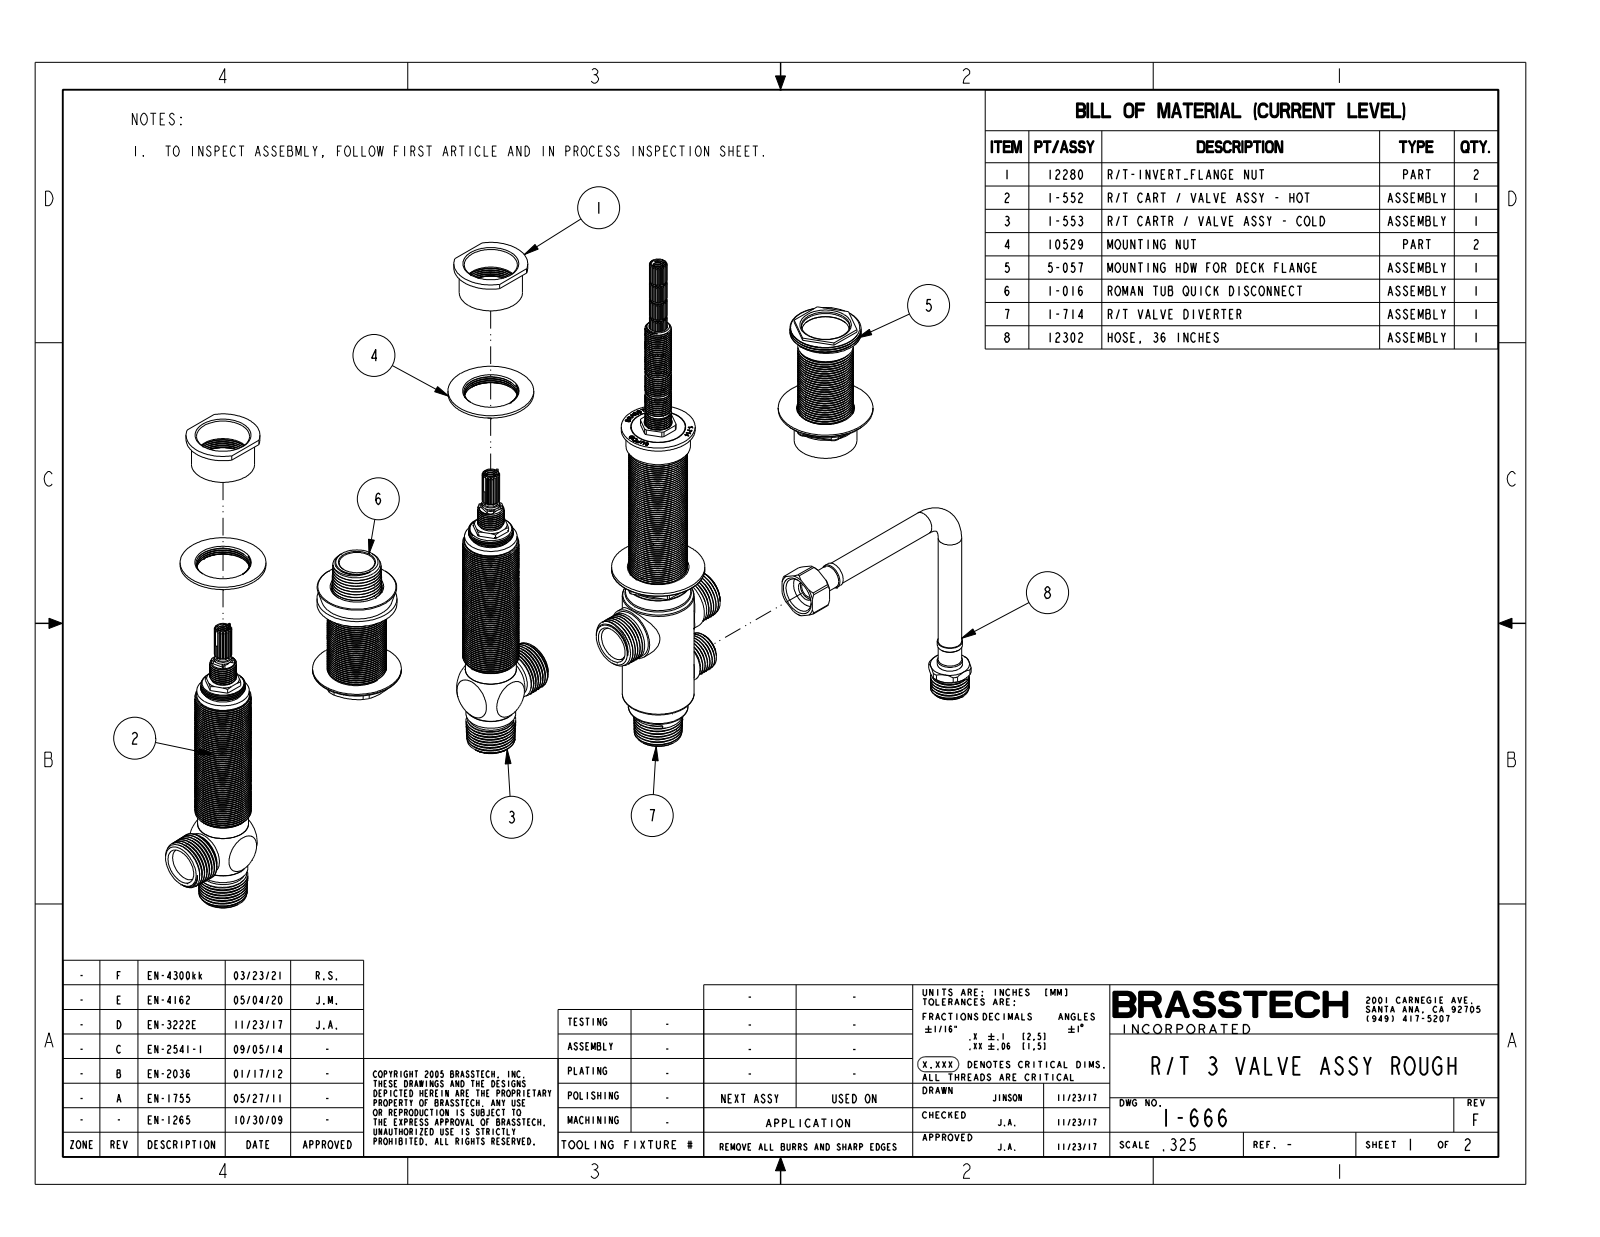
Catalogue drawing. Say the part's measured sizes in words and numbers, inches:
The part is named "12280; 1-017; 1-004; 1-552_ASM (+8 more)". Its 3-D file was written by "PRO/ENGINEER BY PARAMETRIC TECHNOLOGY CORPORATION, 2013150 (CONFIG_CONTROL_DESIGN)". It is 39 solids with 4378 faces: 1033 planar, 1963 cylindrical and 1382 other. Overall it measures 22.299 by 15.517 by 2.821 inches. Its volume is 25.97 cubic inches and its surface area 530.8 square inches. Round holes: 3 of diameter 0.77, 2 of diameter 0.196, 2 of diameter 0.201, 2 of diameter 0.23, 2 of diameter 0.477, 2 of diameter 0.535, 2 of diameter 0.63, 2 of diameter 0.665, 2 of diameter 0.75, 2 of diameter 0.78, 2 of diameter 0.8, 2 of diameter 0.83. Round bosses or shafts: 4 of diameter 0.043, 2 of diameter 1.811, 2 of diameter 1.35, 2 of diameter 1.187, 2 of diameter 1.11, 2 of diameter 1.04, 2 of diameter 1.034, 2 of diameter 0.985. Partial cylindrical surfaces (rounded edges, fillets, slot ends): 25 of radius 0.004, 17 of radius 0.04, 14 of radius 0.008, 10 of radius 0.08, 8 of radius 0.02, 6 of radius 0.02, 6 of radius 0.15, 4 of radius 0.079. The main face-to-face distances are 0.138, 1.411, 3.11, 1.699, 3, 1.589, 0.11, 1.45, 0.039, 1.55. The hole center spacings are 4, 5, 0.418, 1.065, 2.886, 4.714, 5.304, 7.43.
